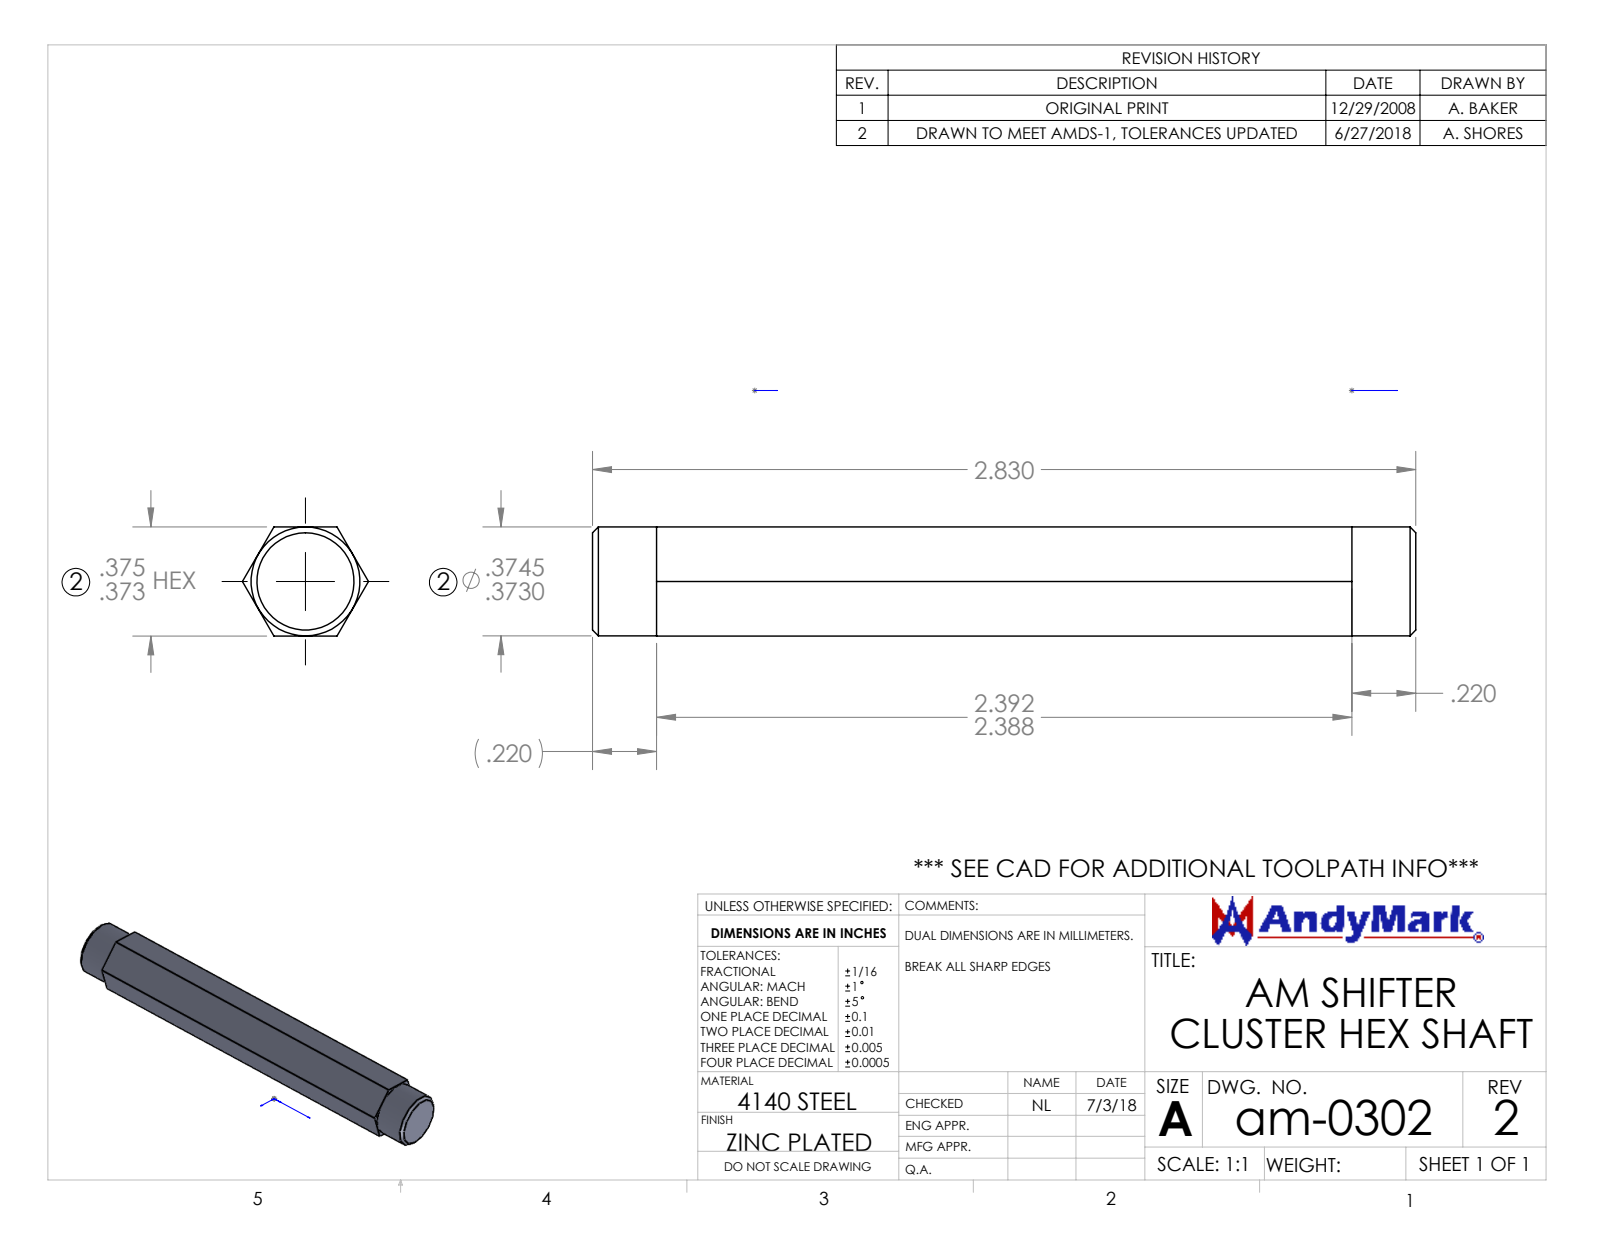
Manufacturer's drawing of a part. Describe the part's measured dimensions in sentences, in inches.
The part is named "am-0302 AM Shifter Cluster Hex Shaft REV2". Its 3-D file was written by "SolidWorks 2018 (AUTOMOTIVE_DESIGN)". It is 1 solid with 18 faces: 10 planar, 4 cylindrical and 4 other. Overall it measures 2.83 by 0.433 by 0.375 inches. Its volume is 0.339 cubic inches and its surface area 3.837 square inches. Round bosses or shafts: 1 of diameter 0.374. The main face-to-face distances are 0.375, 0.375, 2.83, 0.22, 2.61, 2.61, 2.39, 0.22.
